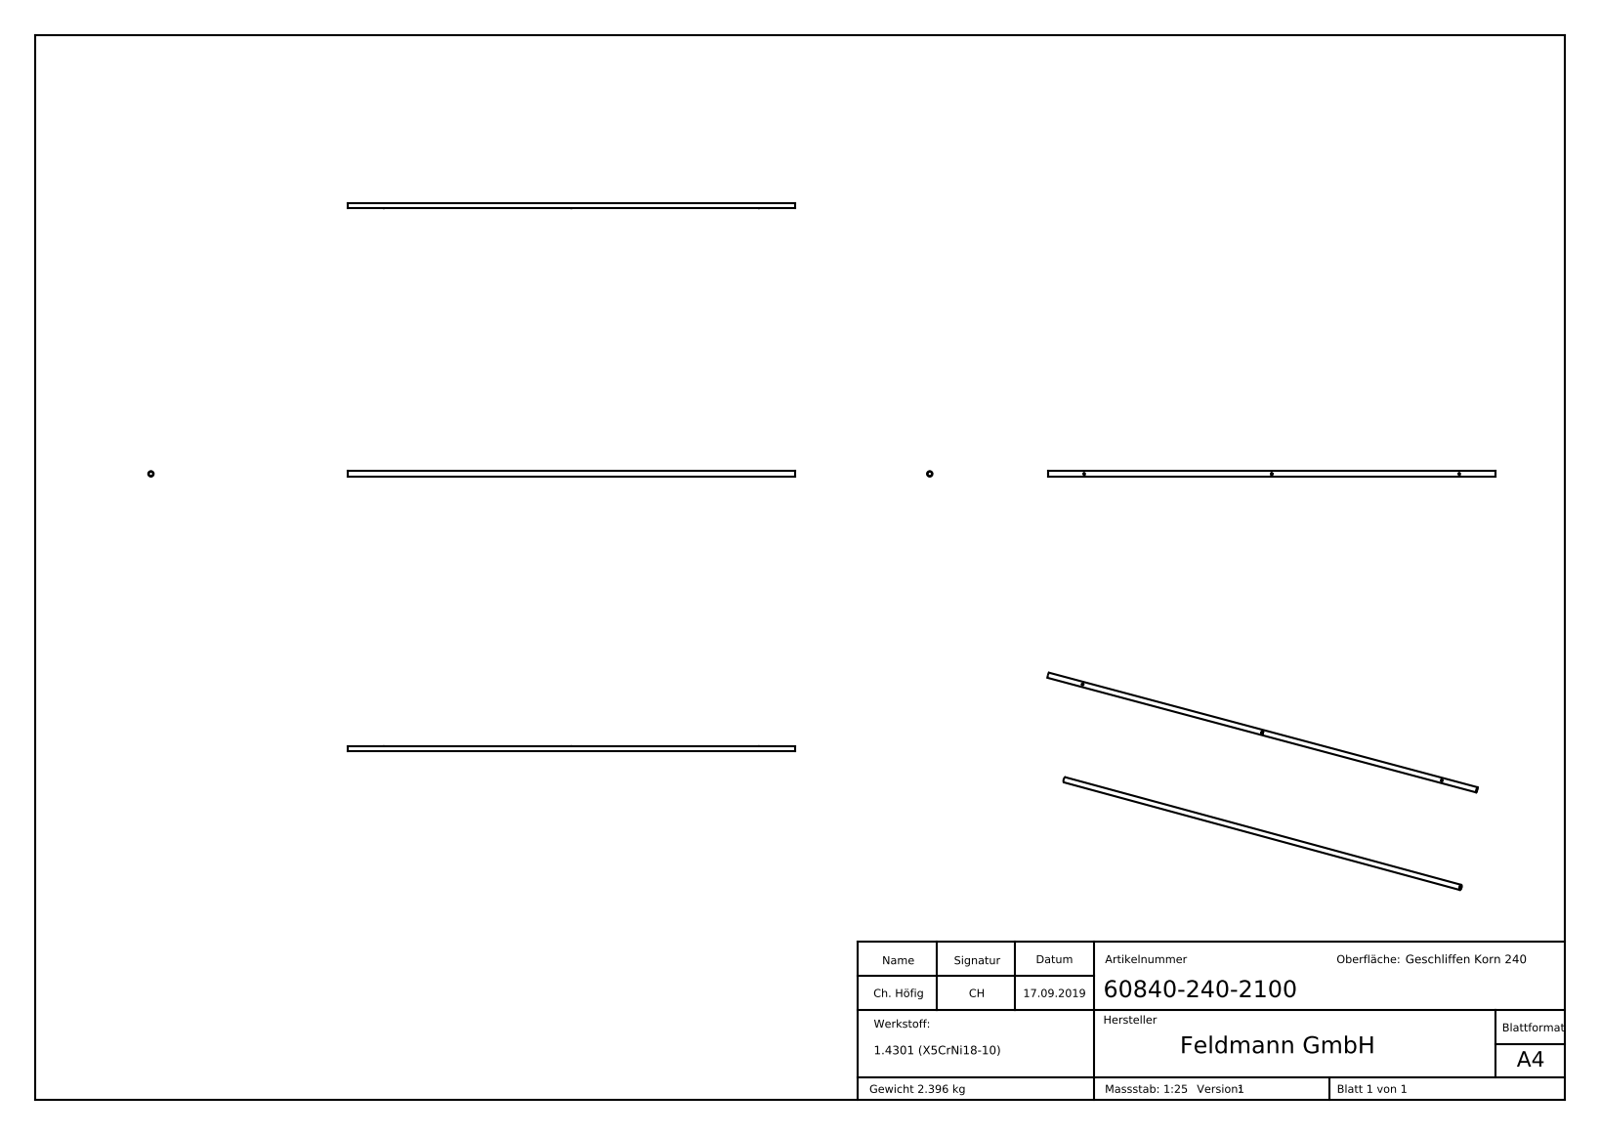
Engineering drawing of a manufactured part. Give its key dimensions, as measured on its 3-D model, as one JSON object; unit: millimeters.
{"part_name": "60840-240-2100", "step_written_by": "SolidWorks 2015 (CONFIG_CONTROL_DESIGN)", "units": "millimeters", "bodies": {"solids": 1, "faces": 296, "planar": 111, "cylindrical": 54, "other": 131}, "overall_size": [2100, 25, 25], "volume_mm3": 303257, "surface_area_mm2": 303690, "round_holes": [[6.8, 3], [21, 1]], "round_bosses_or_shafts": [[25, 1]], "partial_cylinders_radius": [[10.6, 1]], "face_to_face_distances": [2100, 0.44, 0.39, 2.97, 3.66, 3.27, 8.4, 2.67, 0.61, 3.44], "hole_center_spacings": [880, 1760]}
